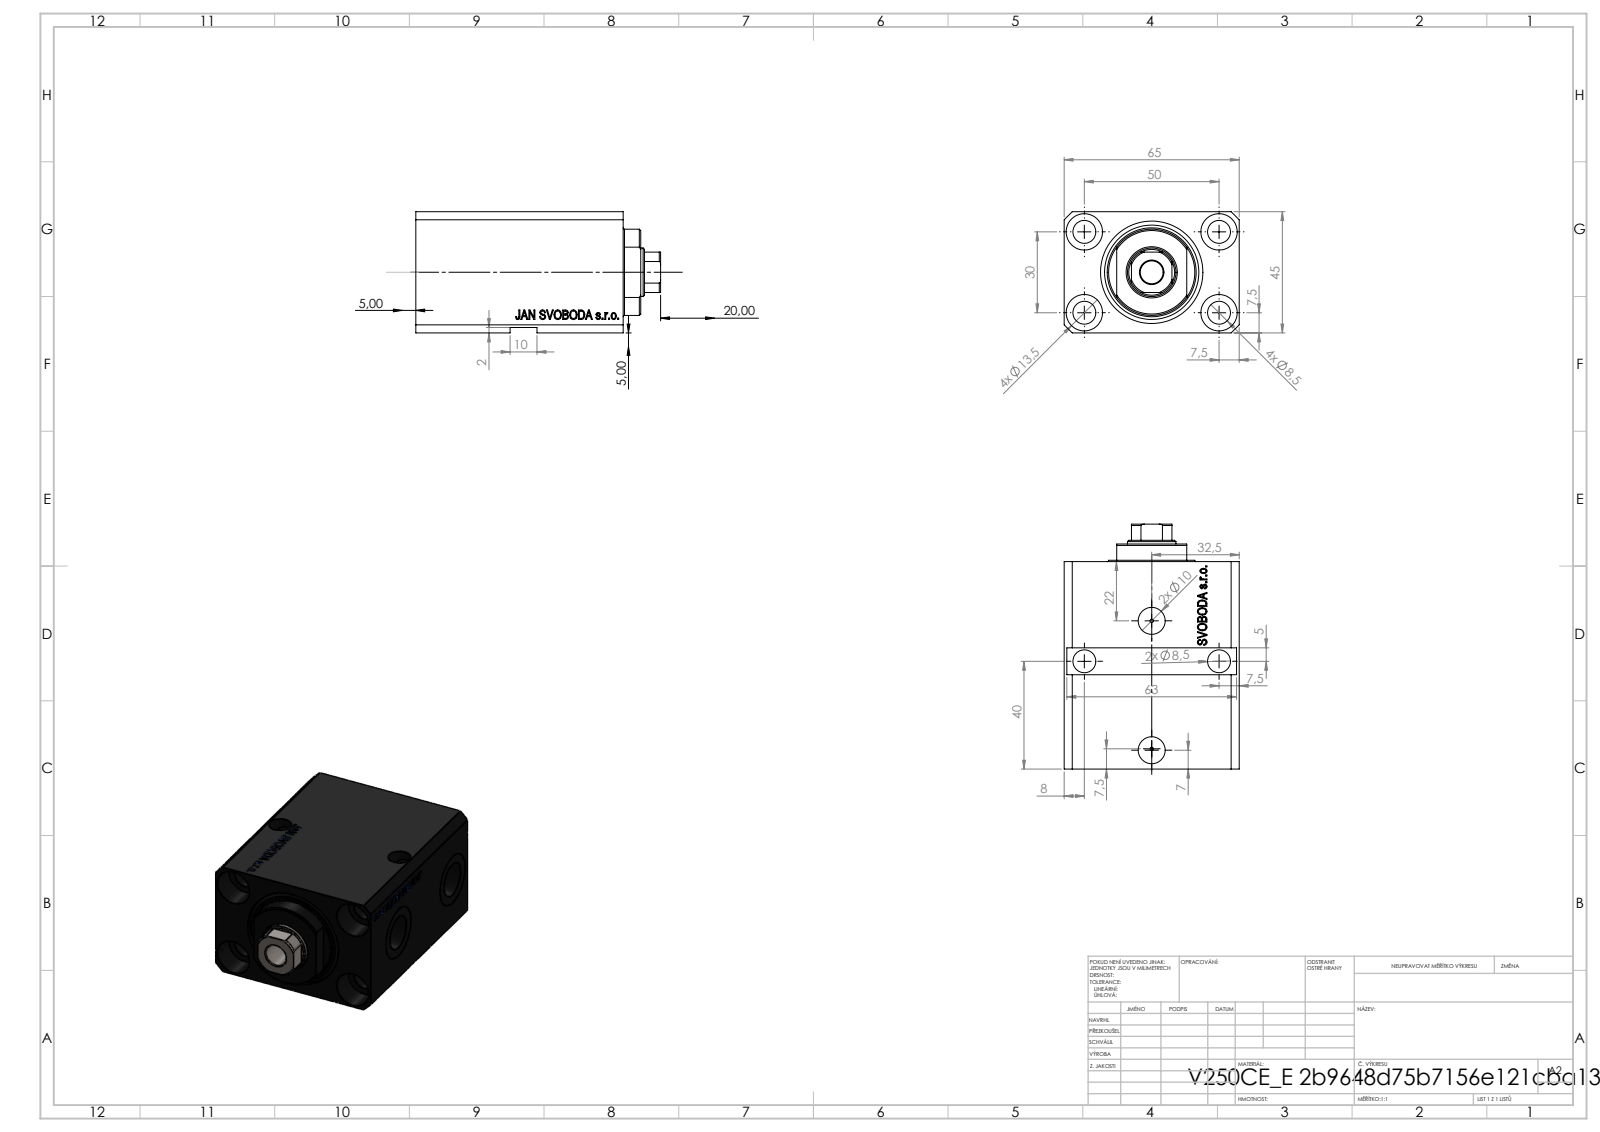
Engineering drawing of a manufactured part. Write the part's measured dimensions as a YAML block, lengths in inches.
part_name: "V250CE_C_VCP; V250CE_VC_E; V250CE_E_Body"
step_written_by: "SolidWorks 2019 (CONFIG_CONTROL_DESIGN)"
units: inches
bodies: {solids: 3, faces: 897, planar: 435, cylindrical: 84, other: 378}
overall_size: [3.583, 2.559, 1.772]
volume: 11.7
surface_area: 81
round_holes:
  - {diameter: 0.335, count: 7}
  - {diameter: 0.049, count: 4}
  - {diameter: 0.531, count: 4}
  - {diameter: 0.394, count: 2}
  - {diameter: 0.518, count: 2}
  - {diameter: 0.787, count: 2}
  - {diameter: 0.709, count: 1}
  - {diameter: 0.984, count: 1}
  - {diameter: 1.496, count: 1}
partial_cylinders:
  - {radius: 0.335, count: 1}
  - {radius: 0.63, count: 1}
face_to_face_distances: [1.772, 2.559, 2.48, 0.551, 3.031, 0.272, 2.209, 2.76, 1.693, 0.354]
hole_center_spacings: [1.148, 1.969, 1.181, 1.613, 1.63, 2.296, 0.021, 1.693]
